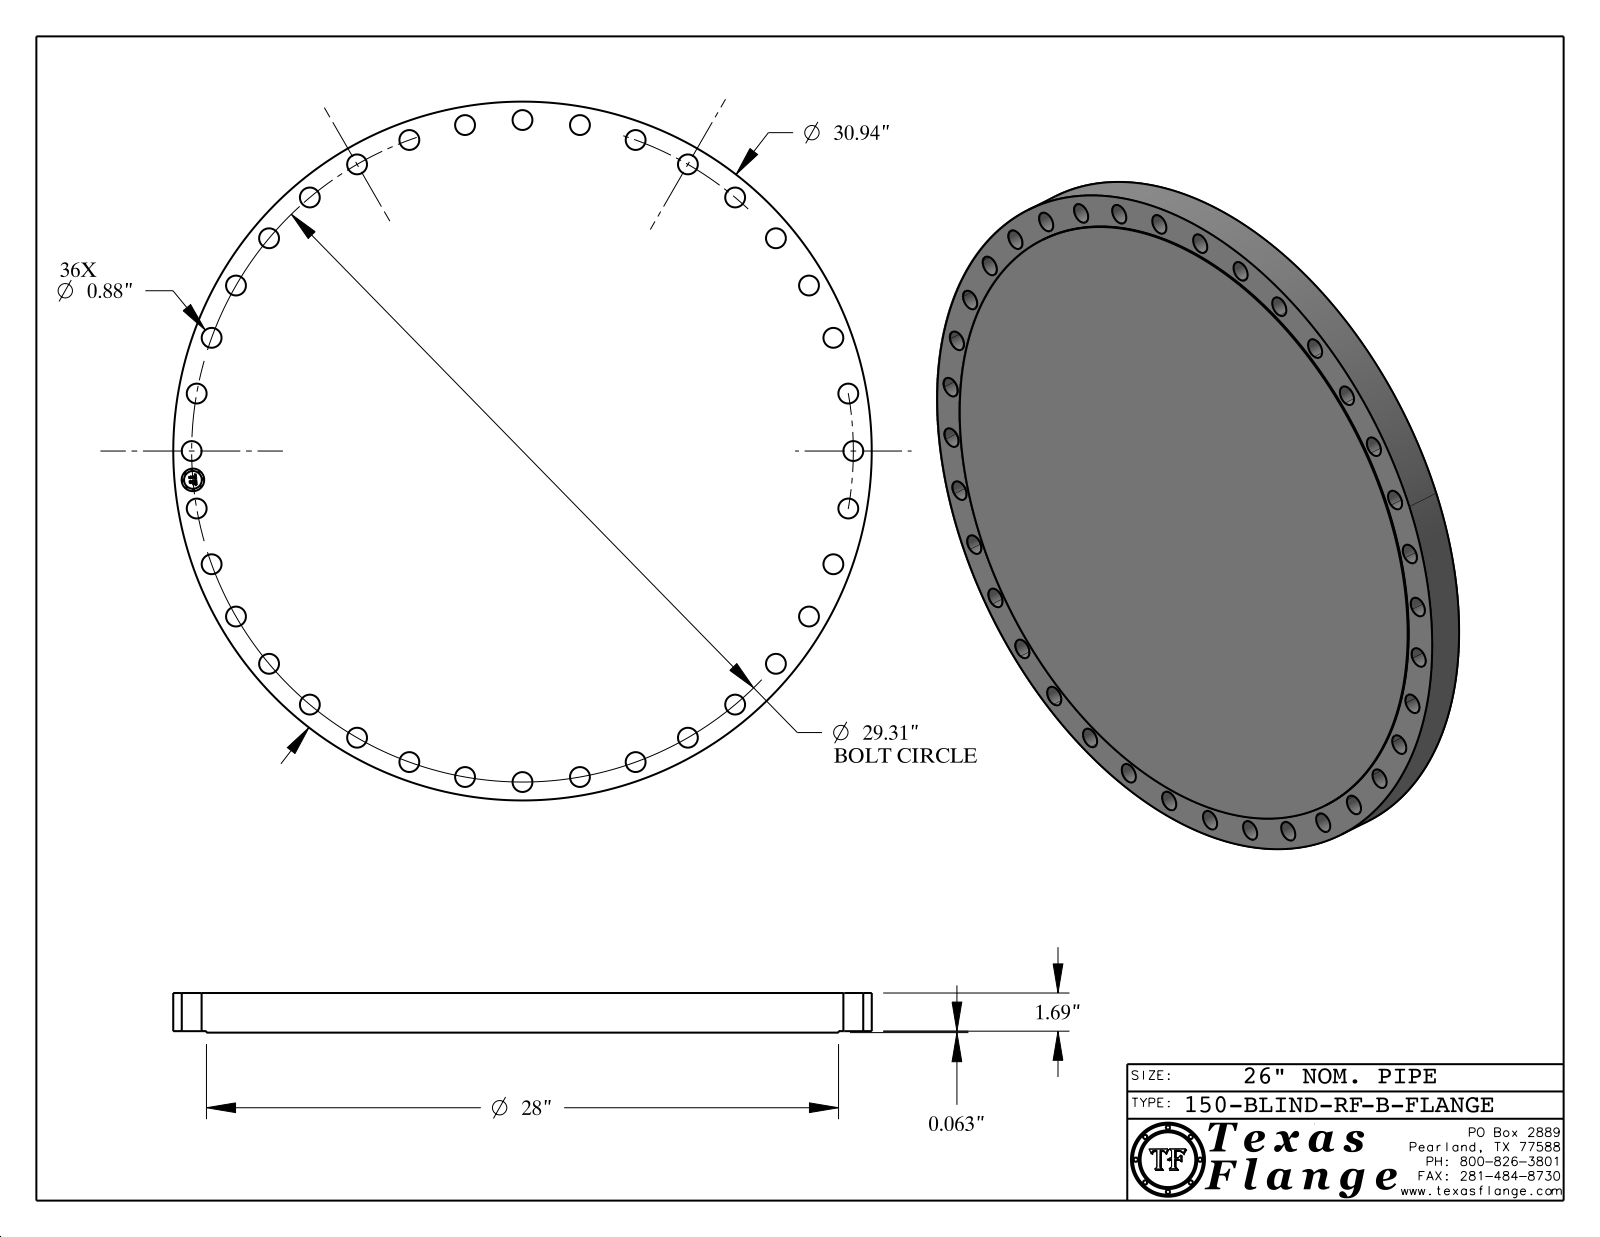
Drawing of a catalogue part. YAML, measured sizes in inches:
part_name: "150-BLIND-RF, Series B"
step_written_by: "CATIA V5 STEP AP214 (AUTOMOTIVE_DESIGN)"
units: inches
bodies: {solids: 1, faces: 464, planar: 368, cylindrical: 96, other: 0}
overall_size: [30.94, 30.94, 1.753]
volume: 1272
surface_area: 1798
round_holes:
  - {diameter: 0.88, count: 36}
  - {diameter: 1, count: 1}
round_bosses_or_shafts:
  - {diameter: 0.061, count: 8}
  - {diameter: 30.94, count: 1}
  - {diameter: 28, count: 1}
  - {diameter: 0.788, count: 1}
face_to_face_distances: [1.753, 0.063, 1.69, 1.738, 1.675, 0.015, 0.298, 0.293, 0.054, 0.193]
hole_center_spacings: [28.311, 12.387, 14.655, 18.84, 24.009, 27.543, 29.198, 2.555]
